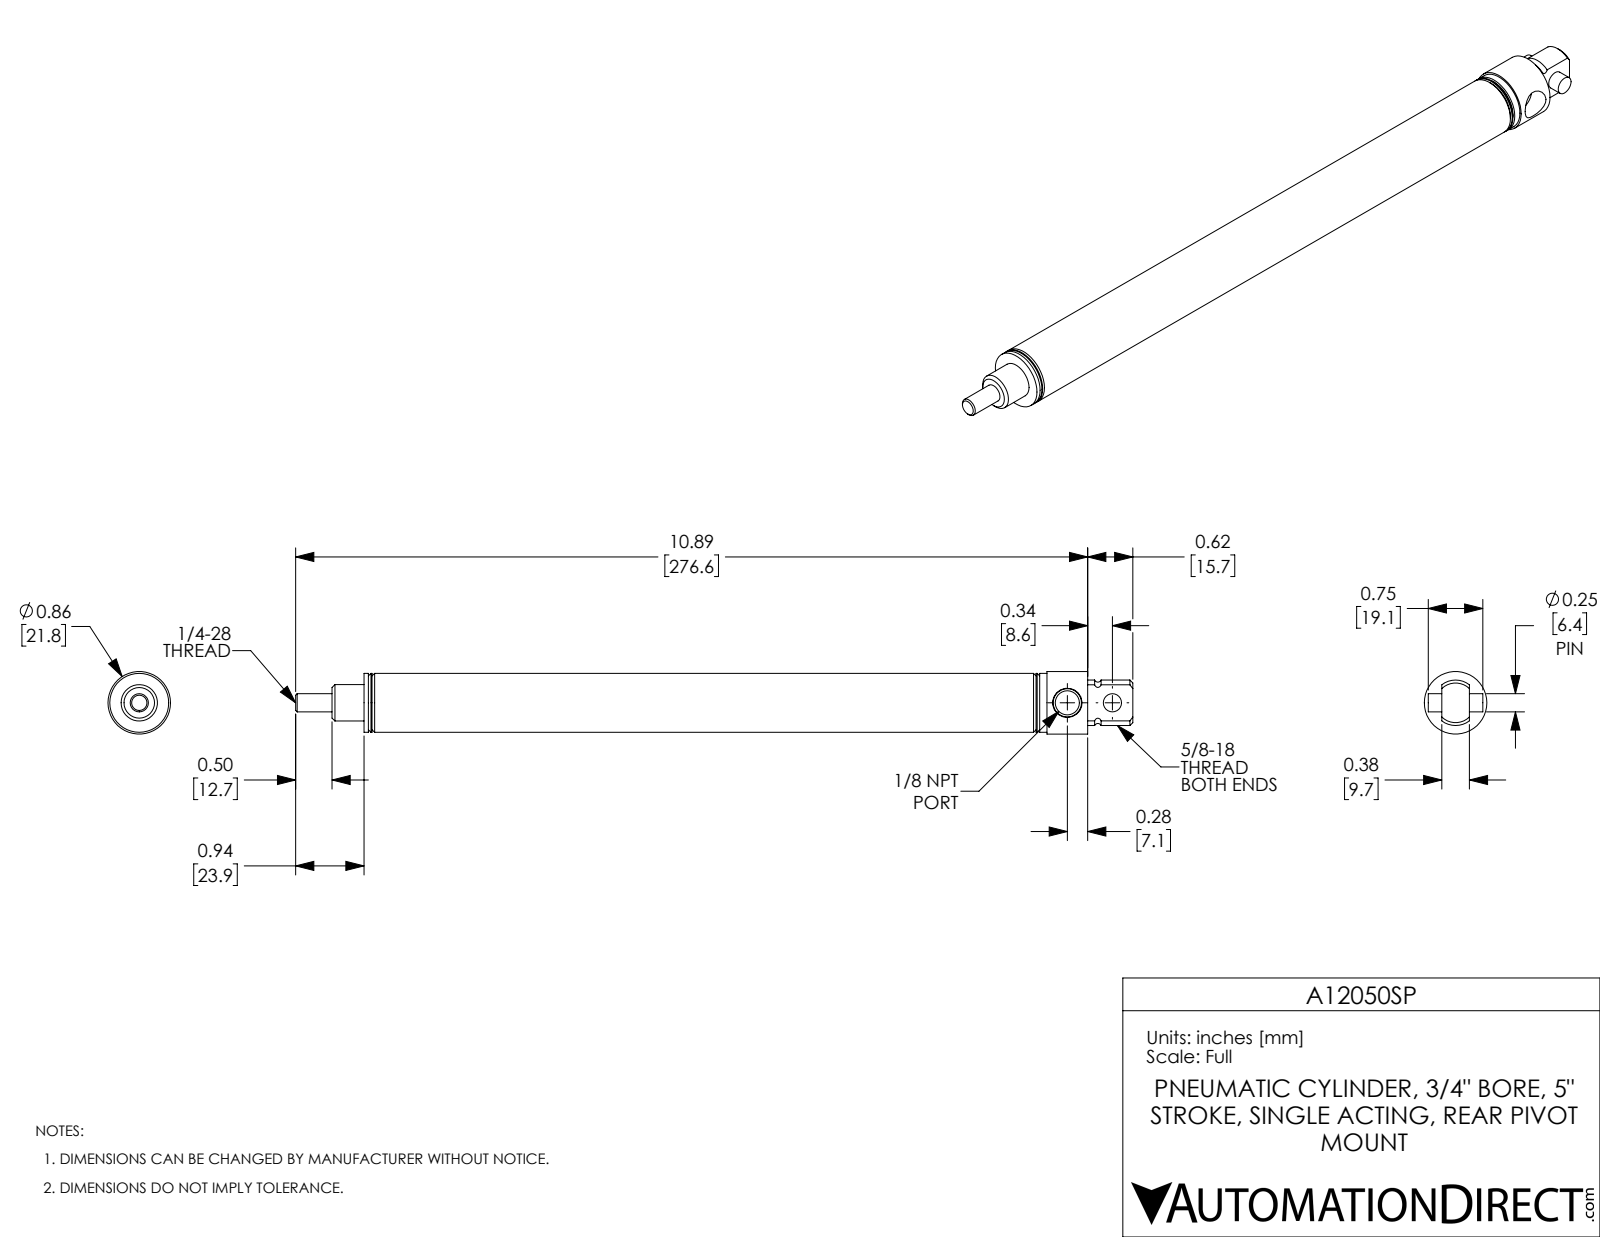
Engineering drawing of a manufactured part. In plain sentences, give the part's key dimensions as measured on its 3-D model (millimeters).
The part is named "A12050SP; A12050SP-Pin; A12050SP-Rod; A12050SP-MainBody". Its 3-D file was written by "SolidWorks 2017 (AUTOMOTIVE_DESIGN)". It is 3 solids with 73 faces: 19 planar, 32 cylindrical and 22 other. Overall it measures 292.4 by 21.8 by 21.8 millimeters. Its volume is 55 830 cubic millimeters and its surface area 35 150 square millimeters. Round holes: 2 of diameter 6.4, 1 of diameter 8.4, 1 of diameter 19.1. Round bosses or shafts: 1 of diameter 21.8, 1 of diameter 20.6, 1 of diameter 12.7. Partial cylindrical surfaces (rounded edges, fillets, slot ends): 1 of radius 8. The main face-to-face distances are 12.7, 139.7, 127, 56.5, 69.2, 196.2, 252.7, 196.2, 183.5, 56.5. The hole center spacings are 15.7.
